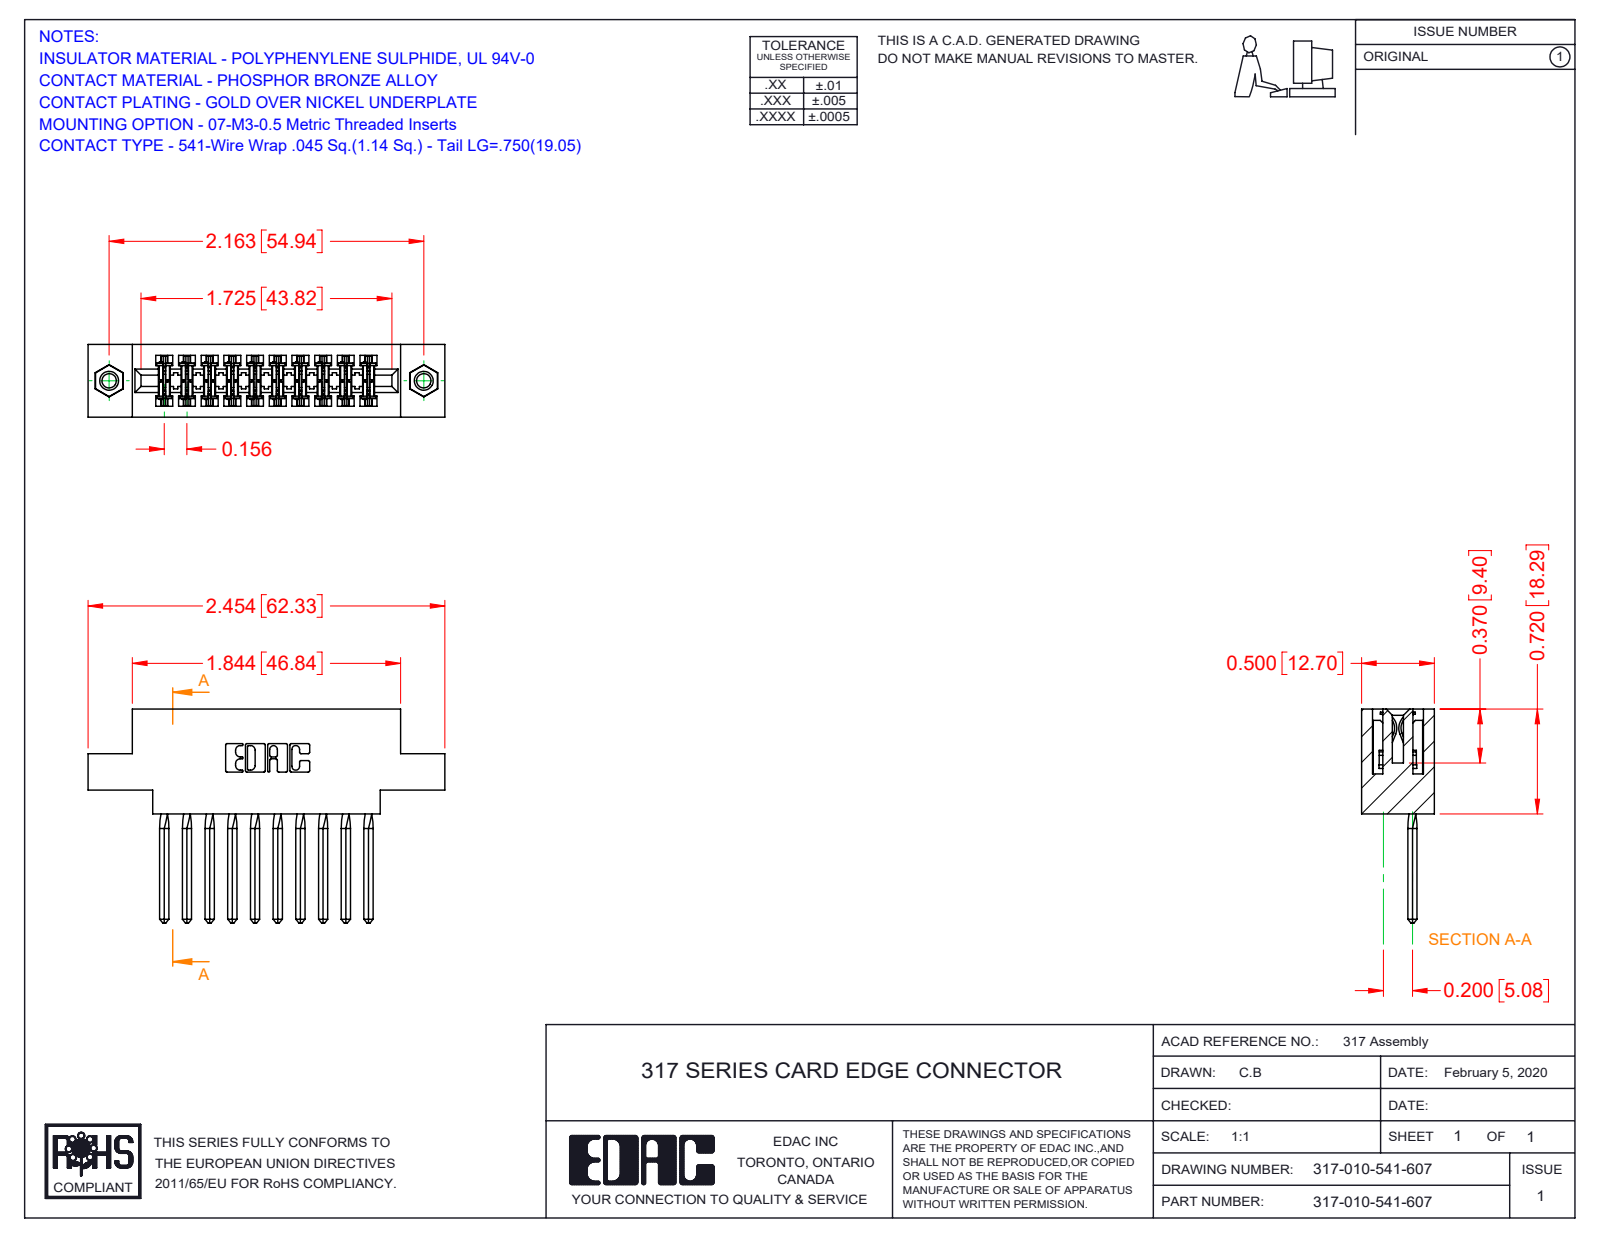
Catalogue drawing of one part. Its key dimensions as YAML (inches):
part_name: "345-250-001_345-250-005-103; 317-010-541-607; 317-290-002_541; 317 Part_.156 Dia - TI"
step_written_by: "SolidWorks 2016 (CONFIG_CONTROL_DESIGN)"
units: inches
bodies: {solids: 13, faces: 1682, planar: 1330, cylindrical: 296, other: 56}
overall_size: [2.454, 1.47, 0.5]
volume: 0.556
surface_area: 18.36
round_holes:
  - {diameter: 0.098, count: 2}
  - {diameter: 0.125, count: 2}
  - {diameter: 0.156, count: 2}
round_bosses_or_shafts:
  - {diameter: 0.155, count: 2}
partial_cylinders:
  - {radius: 0.01, count: 22}
  - {radius: 0.015, count: 20}
  - {radius: 0.007, count: 6}
  - {radius: 0.031, count: 6}
  - {radius: 0.026, count: 3}
  - {radius: 0.095, count: 2}
  - {radius: 0.1, count: 2}
  - {radius: 0.11, count: 2}
face_to_face_distances: [0.5, 0.075, 0.425, 0.11, 0.065, 0.22, 0.331, 0.35, 0.136, 0.156]
hole_center_spacings: [2.163]
